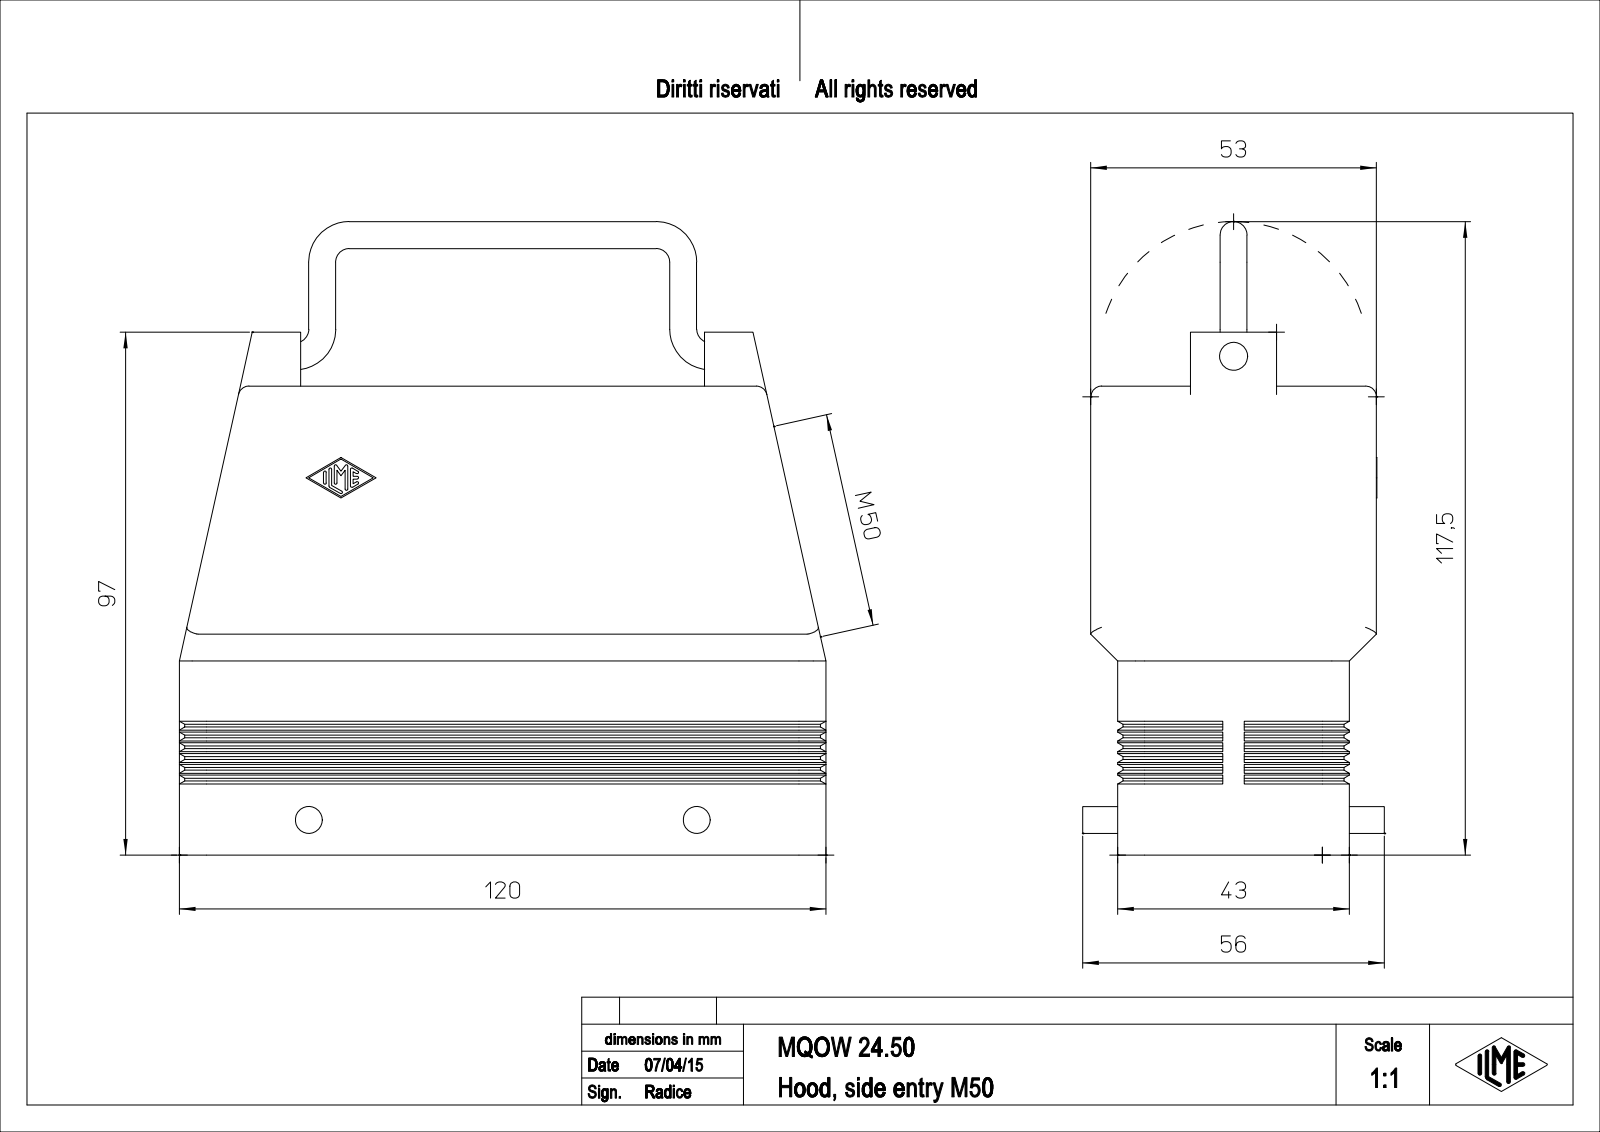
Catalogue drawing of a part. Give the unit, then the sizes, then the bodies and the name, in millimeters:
Units: millimetres
Overall size (bounding box): 120 × 117.5 × 56
Round holes (diameter × count): ⌀2.46 ×4, ⌀5.2 ×1, ⌀50 ×1
Round bosses / shafts (diameter × count): ⌀5 ×6
Partial cylindrical surfaces — rounded edges, fillets, slot ends (radius × count): R2 ×16, R0.25 ×14, R2.5 ×4, R4 ×4, R5 ×4
Main face-to-face distances: 3, 5, 45, 42, 50, 8, 40, 2, 47, 48
Hole centre spacings: 27, 104, 107.45
Volume: 92 780 mm³ · Surface area: 68 082 mm²
Bodies: 1 solid, 428 faces (244 planar, 124 cylindrical, 60 other)
Part name (STEP PRODUCT): MQOW_24.50
STEP written by: PTC Creo Elements/Direct Modeling 19.0E 27-Jun-2016 (C) Parametric Technology GmbH (AUTOMOTIVE_DESIGN)
